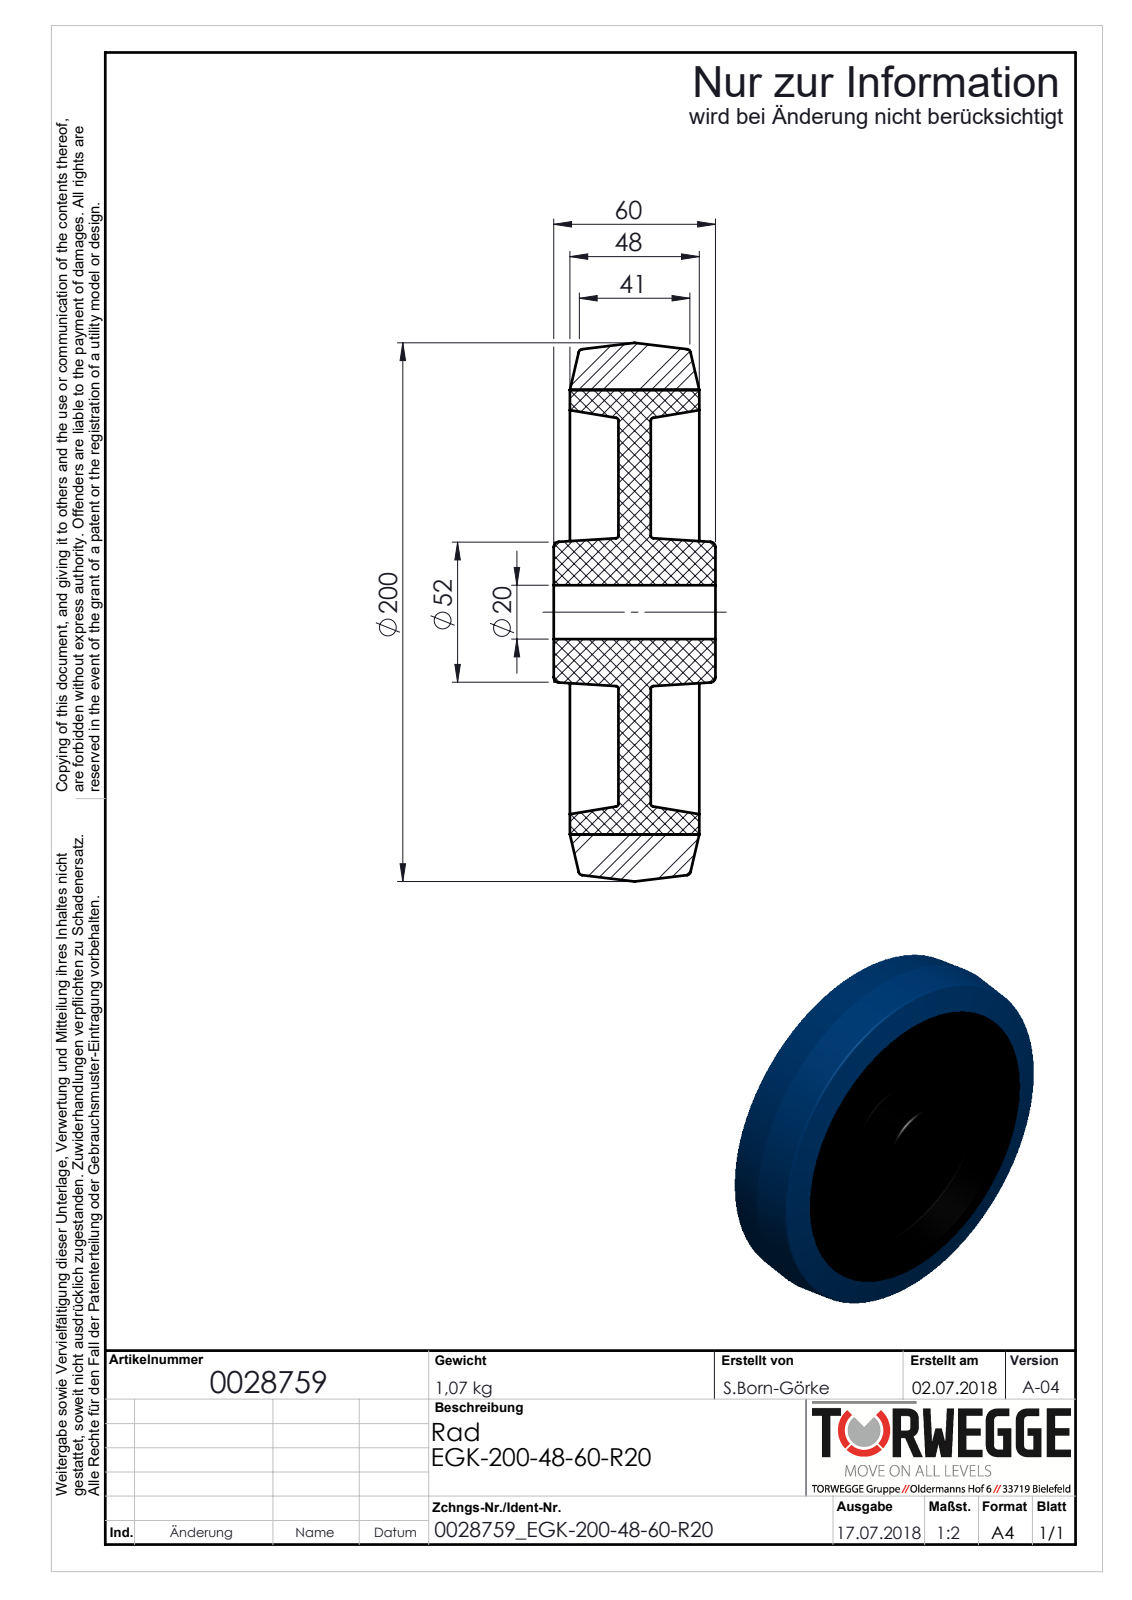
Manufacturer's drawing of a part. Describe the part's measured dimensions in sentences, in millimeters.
The part is named "0028759K_ER_200_48_4R_C". Its 3-D file was written by "SolidWorks 2012 (AUTOMOTIVE_DESIGN)". It is 1 solid with 40 faces: 6 planar, 2 cylindrical and 32 other. Overall it measures 200 by 200 by 60 millimeters. Its volume is 912 390 cubic millimeters and its surface area 109 654 square millimeters. Round holes: 1 of diameter 20. The main face-to-face distances are 12, 18, 30, 48, 6, 24, 36, 54, 60.
